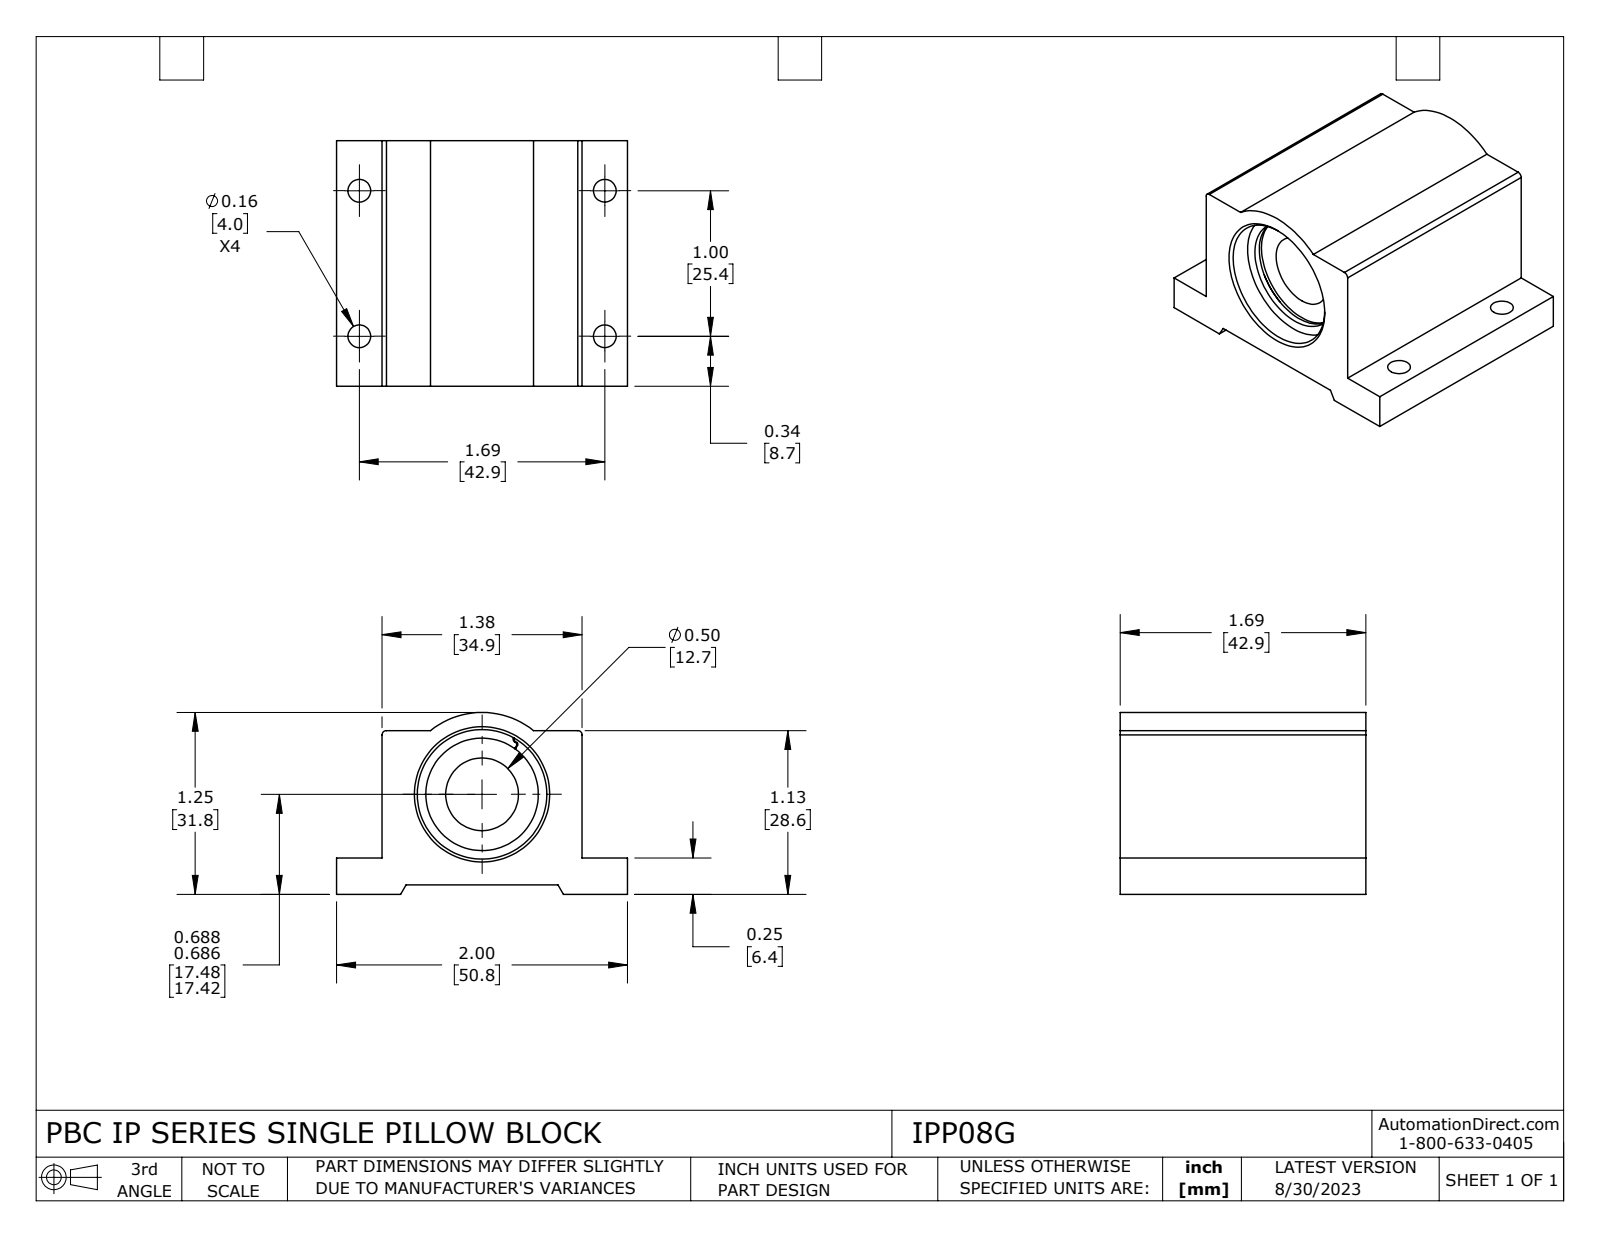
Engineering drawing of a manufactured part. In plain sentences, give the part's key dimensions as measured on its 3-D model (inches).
The part is named "IPP08G". Its 3-D file was written by "SolidWorks 2021 (CONFIG_CONTROL_DESIGN)". It is 4 solids with 126 faces: 43 planar, 63 cylindrical and 20 other. Overall it measures 2 by 1.688 by 1.25 inches. Its volume is 2.292 cubic inches and its surface area 25.9 square inches. Round holes: 4 of diameter 0.156, 1 of diameter 0.5, 1 of diameter 0.773, 1 of diameter 0.783, 1 of diameter 0.89, 1 of diameter 0.931. Round bosses or shafts: 1 of diameter 0.943, 1 of diameter 0.875, 1 of diameter 0.821. Partial cylindrical surfaces (rounded edges, fillets, slot ends): 4 of radius 0.014, 2 of radius 0.009, 2 of radius 0.019, 2 of radius 0.03, 1 of radius 0.563. The main face-to-face distances are 1.375, 0.065, 1.125, 1.06, 1.688, 0.25, 0.185, 0.875, 0.313, 1.687. The hole center spacings are 1, 1.687, 1.961.
